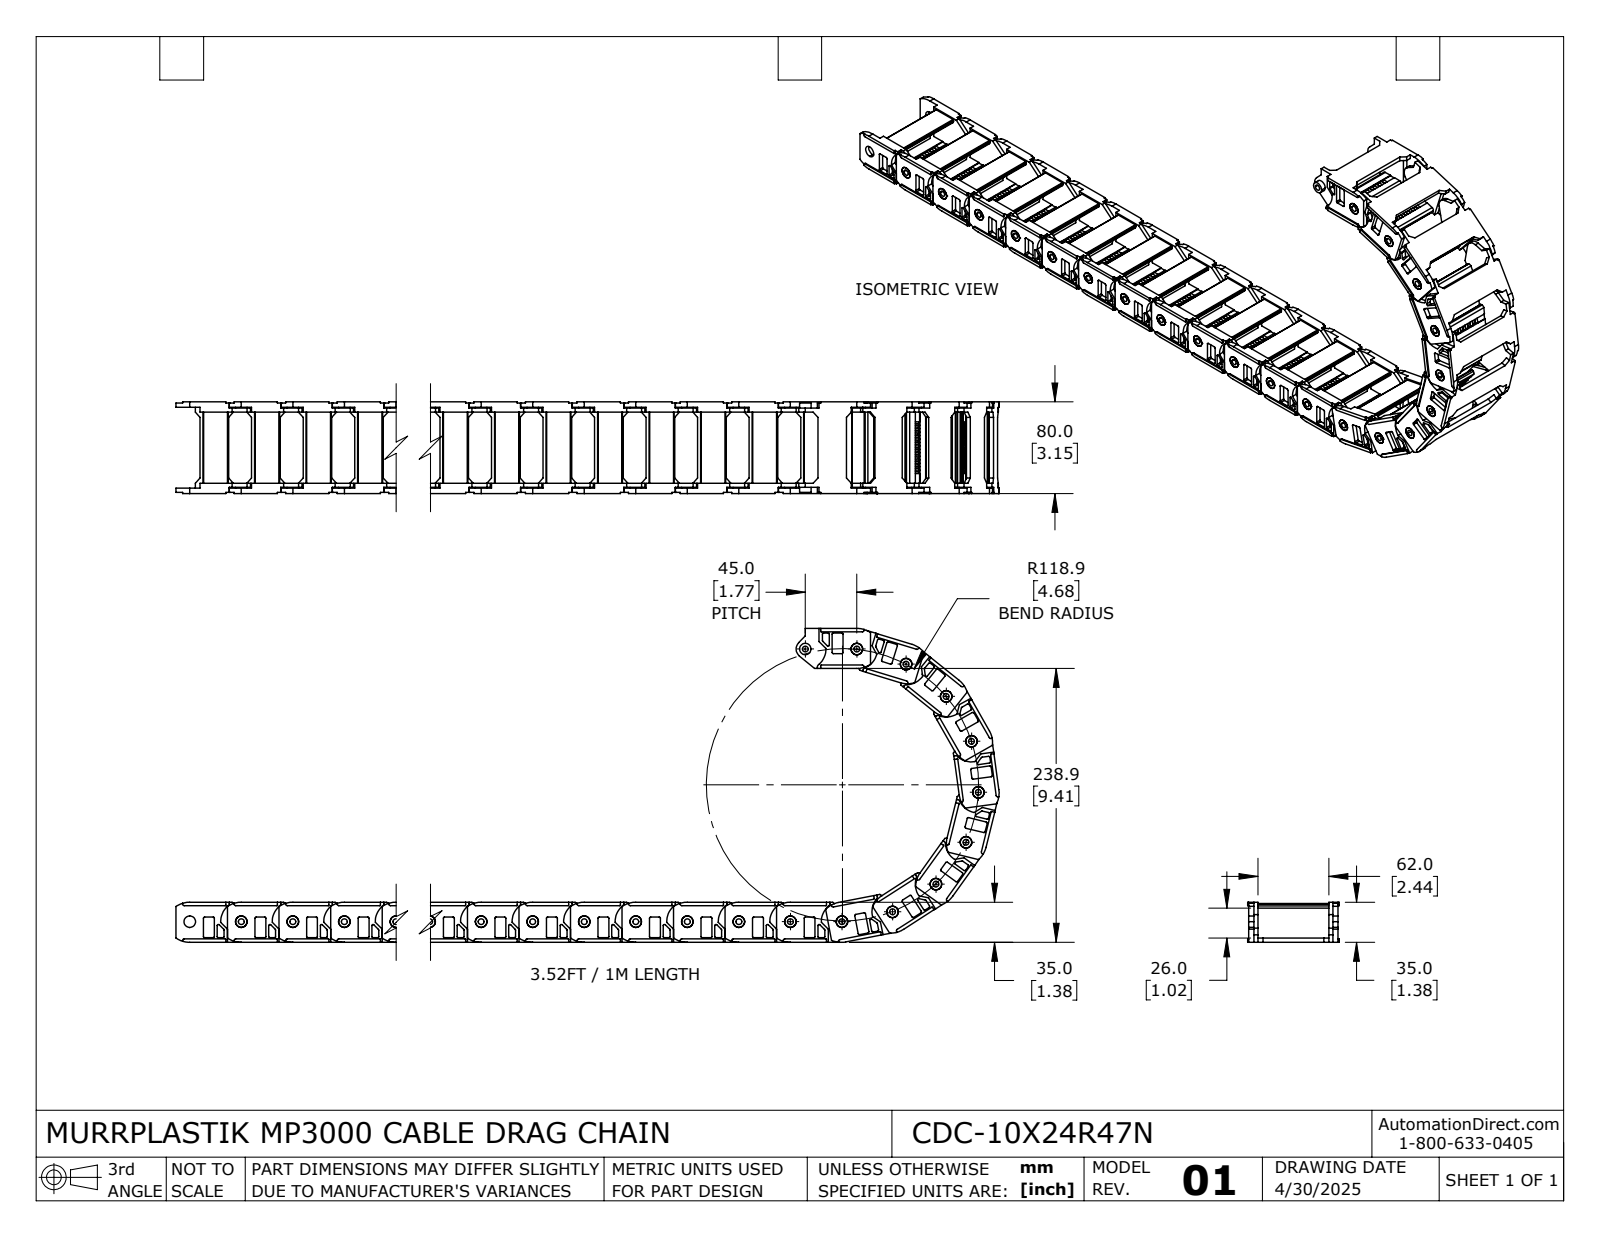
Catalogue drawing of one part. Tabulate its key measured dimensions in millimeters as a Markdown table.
| quantity | value |
| --- | --- |
| part name | CDC-10X24R47N |
| STEP written by | SolidWorks 2024 (AUTOMOTIVE_DESIGN) |
| units | millimeters |
| bodies | 22 solids, 4400 faces (3300 planar, 1100 cylindrical, 0 other) |
| overall size | 734.23 × 274 × 80 |
| volume | 679 888 mm³ |
| surface area | 413 031 mm² |
| round holes (diameter × count) | 5.1 × 22, 10.1 × 22 |
| round bosses / shafts (diameter × count) | 10 × 22 |
| partial cylindrical surfaces (radius × count) | 1 × 176, 0.5 × 88, 1.5 × 44, 2 × 44, 21 × 44, 2.8 × 22, 8 × 22, 18 × 22 |
| main face-to-face distances | 70, 8, 4, 3.7, 74.3, 4.3, 66.3, 62, 3.5, 0.8 |
| hole center spacings | 45, 90, 135, 180, 225, 270, 315, 360 |
